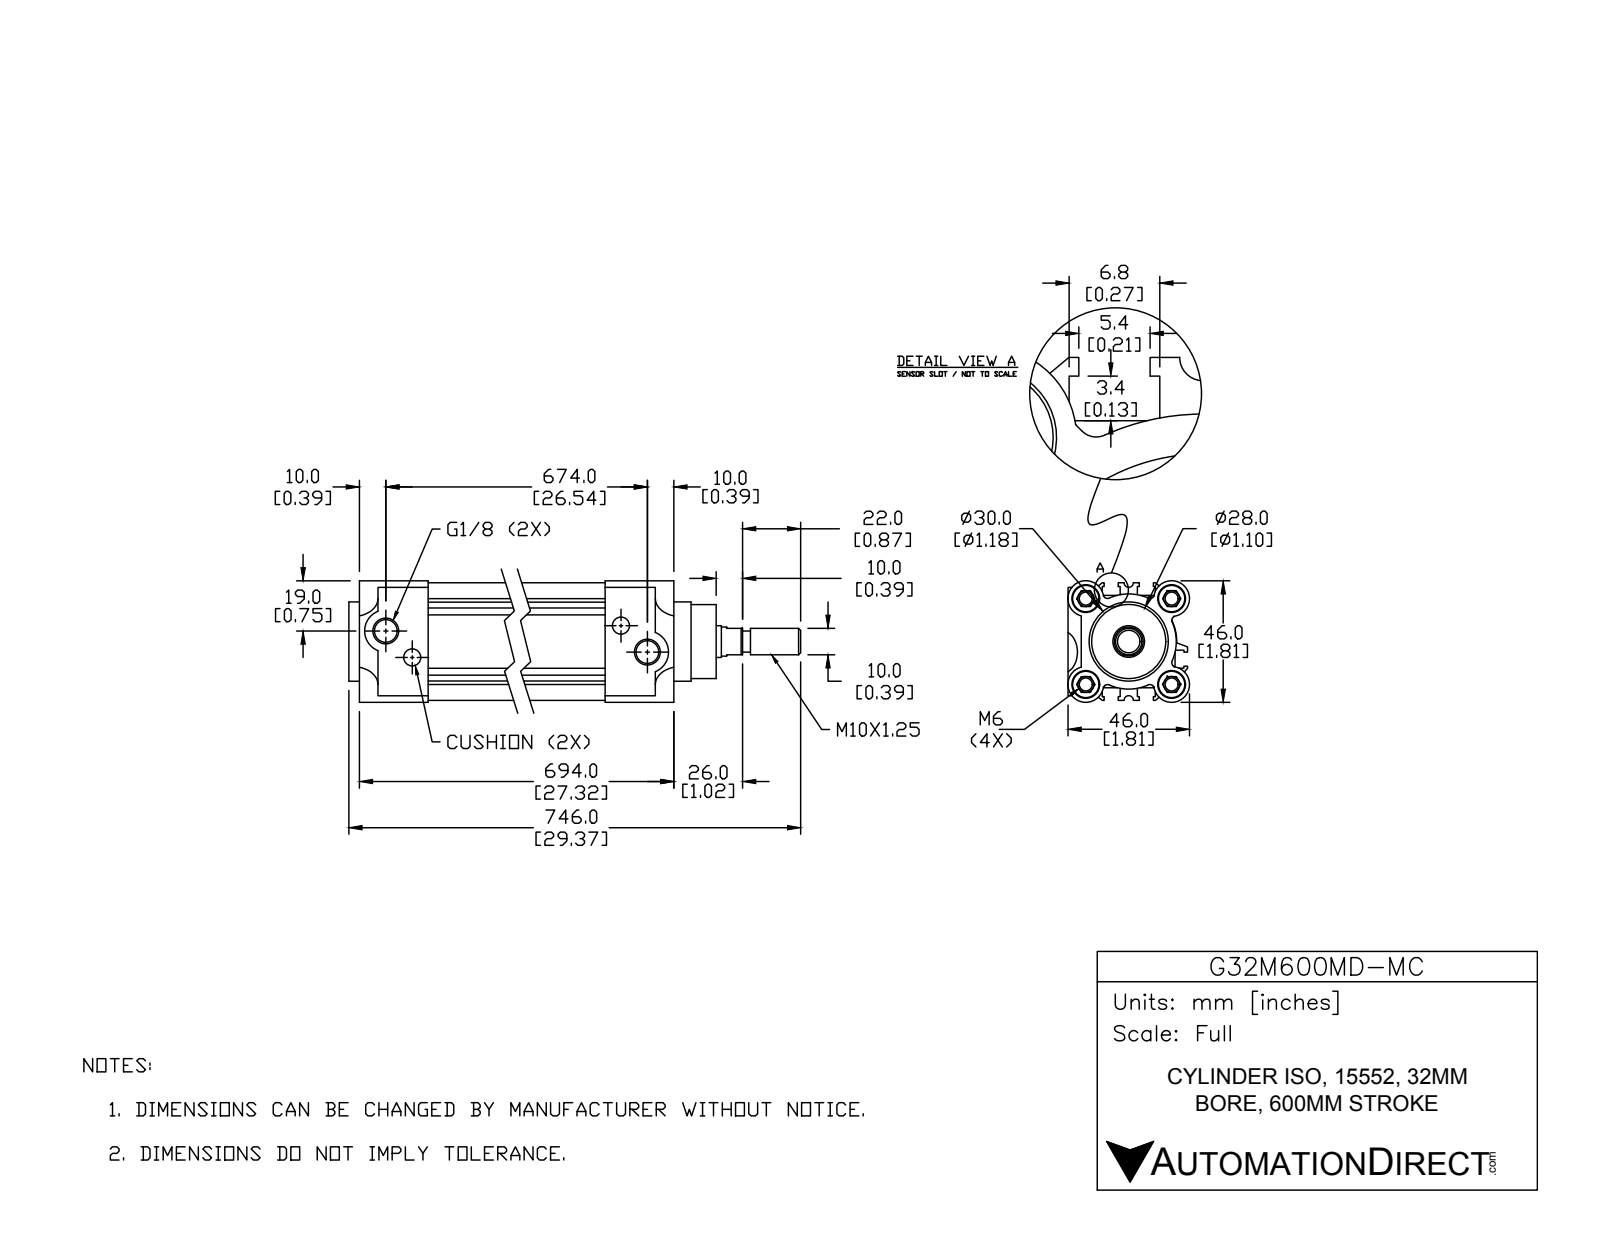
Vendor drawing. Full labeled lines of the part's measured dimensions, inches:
Part name (STEP PRODUCT): 32121-HR; 32-600-73.5-B; G32M600MD-MC; 32121600-R (+1 more)
STEP written by: SolidWorks 2015 (CONFIG_CONTROL_DESIGN)
Units: inches
Bodies: 4 solids, 411 faces (229 planar, 138 cylindrical, 44 other)
Overall size (bounding box): 29.37 × 1.811 × 1.811
Volume: 46.67 in³ · Surface area: 453.1 in²
Round holes (diameter × count): ⌀0.194 ×4, ⌀0.413 ×4, ⌀0.256 ×2, ⌀0.337 ×2, ⌀0.472 ×1
Round bosses / shafts (diameter × count): ⌀0.394 ×5, ⌀1.26 ×1, ⌀1.181 ×1, ⌀1.102 ×1, ⌀0.433 ×1, ⌀0.315 ×1
Partial cylindrical surfaces — rounded edges, fillets, slot ends (radius × count): R0.004 ×12, R0.059 ×6, R0.236 ×4, R0.266 ×4, R0.069 ×2, R0.315 ×2, R0.709 ×1, R0.717 ×1
Main face-to-face distances: 1.565, 0.187, 0.268, 1.004, 0.748, 0.48, 1.272, 1.378, 1.752, 0.524
Hole centre spacings: 0.905, 1.28, 0.557, 1.809, 26.142, 25.752, 26.537
